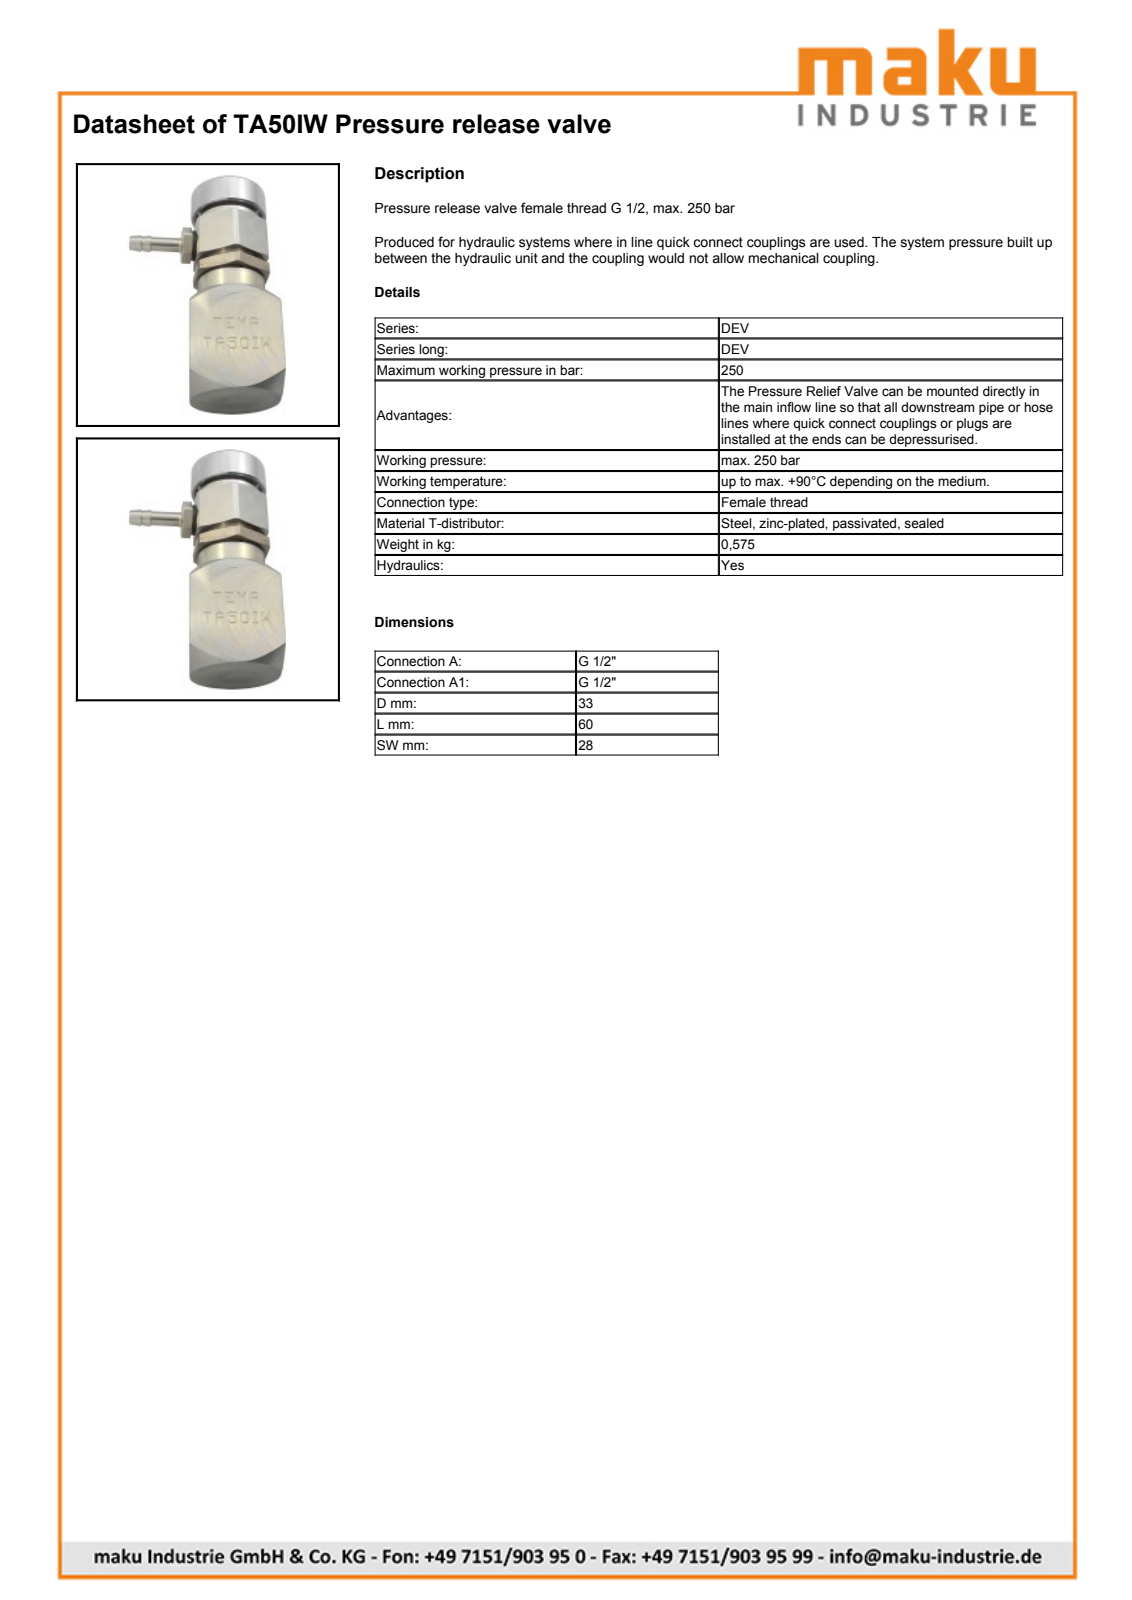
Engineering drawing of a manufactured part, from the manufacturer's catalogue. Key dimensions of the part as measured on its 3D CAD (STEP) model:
Part name (STEP PRODUCT): TA50IW
STEP written by: SolidWorks 2009 (AUTOMOTIVE_DESIGN)
Units: millimetres
Bodies: 1 solid, 177 faces (43 planar, 50 cylindrical, 84 other)
Overall size (bounding box): 98.1 × 53 × 35
Volume: 80 513 mm³ · Surface area: 18 683 mm²
Round holes (diameter × count): ⌀5 ×1, ⌀6 ×1, ⌀7 ×1, ⌀8.6 ×1, ⌀18.63 ×1, ⌀18.63 ×1, ⌀25 ×1
Round bosses / shafts (diameter × count): ⌀33 ×1, ⌀28 ×1, ⌀24.9 ×1, ⌀24 ×1, ⌀23.94 ×1, ⌀20.96 ×1, ⌀8.3 ×1, ⌀6.7 ×1
Partial cylindrical surfaces — rounded edges, fillets, slot ends (radius × count): R8.37 ×1, R16.75 ×1
Main face-to-face distances: 35, 30, 2.5, 32.5, 18.3, 8, 57.3, 60.3, 3, 35.51
Hole centre spacings: 47.9
